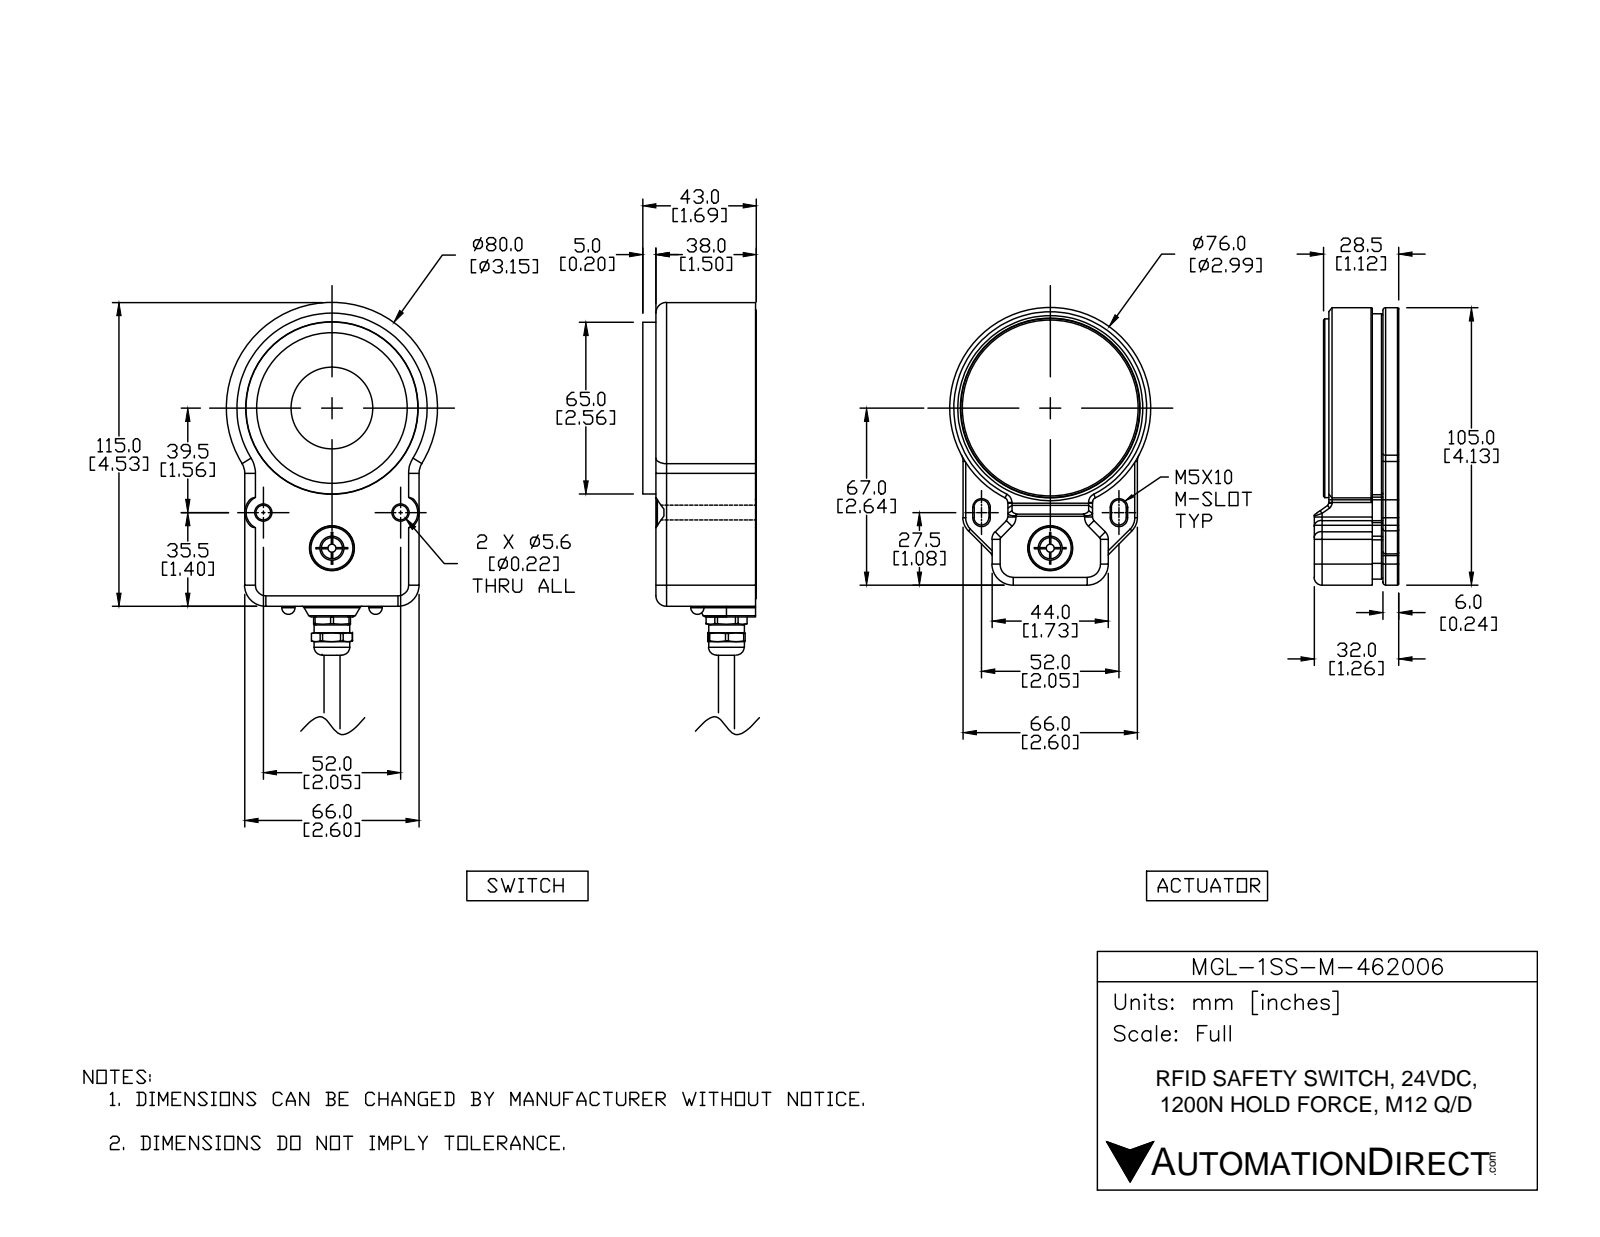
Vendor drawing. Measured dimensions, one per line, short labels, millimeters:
name: MGL-1SS-M-462006; MGL-1SS-M-462006_2; MGL-1SS-M-462006_1
written by: SolidWorks 2017 (AUTOMOTIVE_DESIGN)
unit: mm
bodies: 19 solids, 1647 faces (423 planar, 679 cylindrical, 545 other)
size: 215 × 80 × 72.5
volume: 319 900 mm³; area: 141 900 mm²
holes: 8× ⌀2.5, 6× ⌀3.3, 6× ⌀5, 5× ⌀11.5, 3× ⌀4, 3× ⌀8, 3× ⌀9, 2× ⌀5.6, 2× ⌀7, 1× ⌀6.4, 1× ⌀6.8, 1× ⌀6.8
bosses: 4× ⌀0.5, 2× ⌀12, 2× ⌀5.8, 2× ⌀5.6, 2× ⌀3, 2× ⌀1.2, 1× ⌀76, 1× ⌀71.4
rounds: 188× R0.5, 64× R1, 26× R2, 17× R0.3, 13× R3, 12× R4, 10× R5.5, 7× R0.6
face distances: 6, 8, 2.5, 10.5, 35, 58.5, 28.5, 3, 9, 56
hole spacings: 35.4, 50, 25, 32.5, 39, 20, 34.6, 8.9
